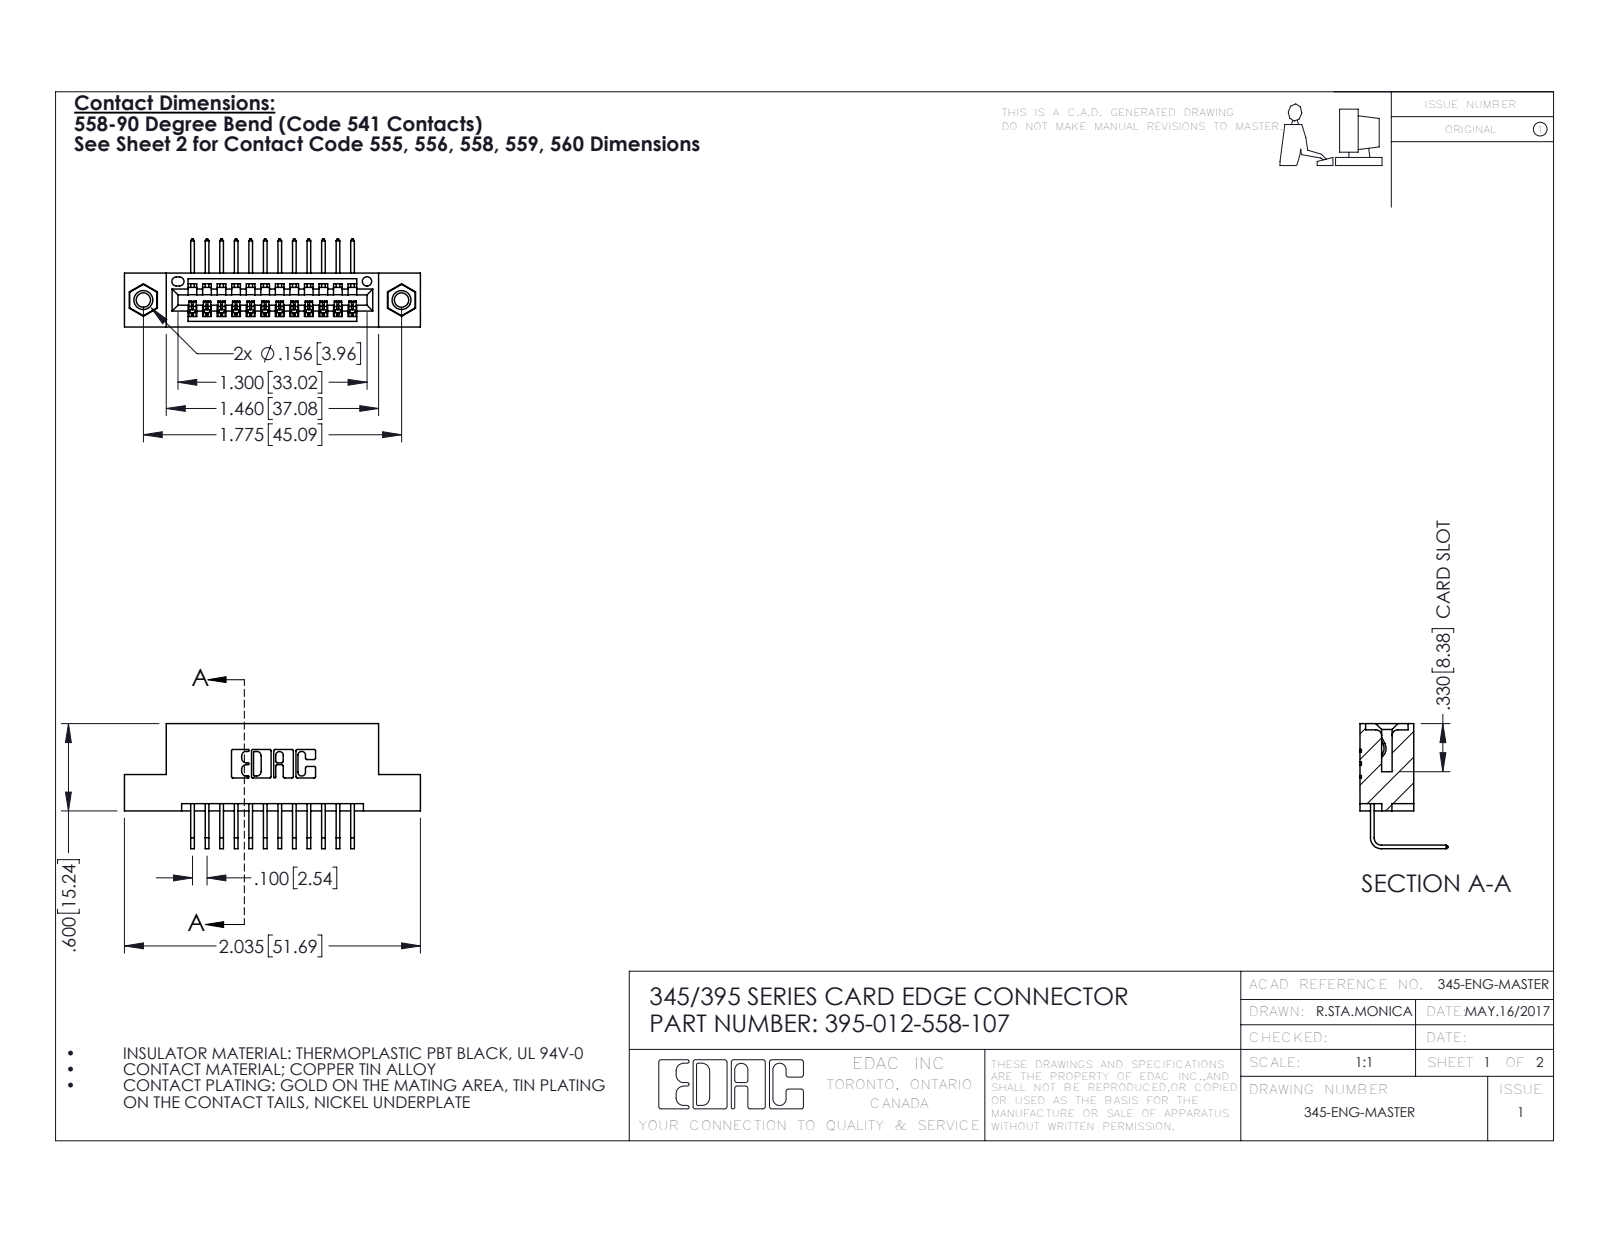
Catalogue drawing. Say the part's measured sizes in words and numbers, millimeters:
The part is named "395-012-558-107; 345-292-001_558 Tail - 2; 345-250-001_345-250-005-103; 345 Part_Flush Mounting Lugs - 0.156 Dia-TI". Its 3-D file was written by "SolidWorks 2016 (CONFIG_CONTROL_DESIGN)". It is 15 solids with 906 faces: 616 planar, 274 cylindrical and 16 other. Overall it measures 51.7 by 21.8 by 15.4 millimeters. Its volume is 4 690 cubic millimeters and its surface area 6 093 square millimeters. Round holes: 2 of diameter 2.5, 2 of diameter 3.2, 2 of diameter 4, 1 of diameter 1.6. Round bosses or shafts: 2 of diameter 3.9. Partial cylindrical surfaces (rounded edges, fillets, slot ends): 24 of radius 0.2, 22 of radius 0.3, 6 of radius 0.2, 6 of radius 0.8, 3 of radius 0.7, 2 of radius 0.8, 2 of radius 1, 1 of radius 0.4. The main face-to-face distances are 5.1, 1.8, 7.6, 9.4, 2.5, 6.9, 0.6, 2.5, 15.2, 7.6. The hole center spacings are 6.9, 39.2, 45.1.
